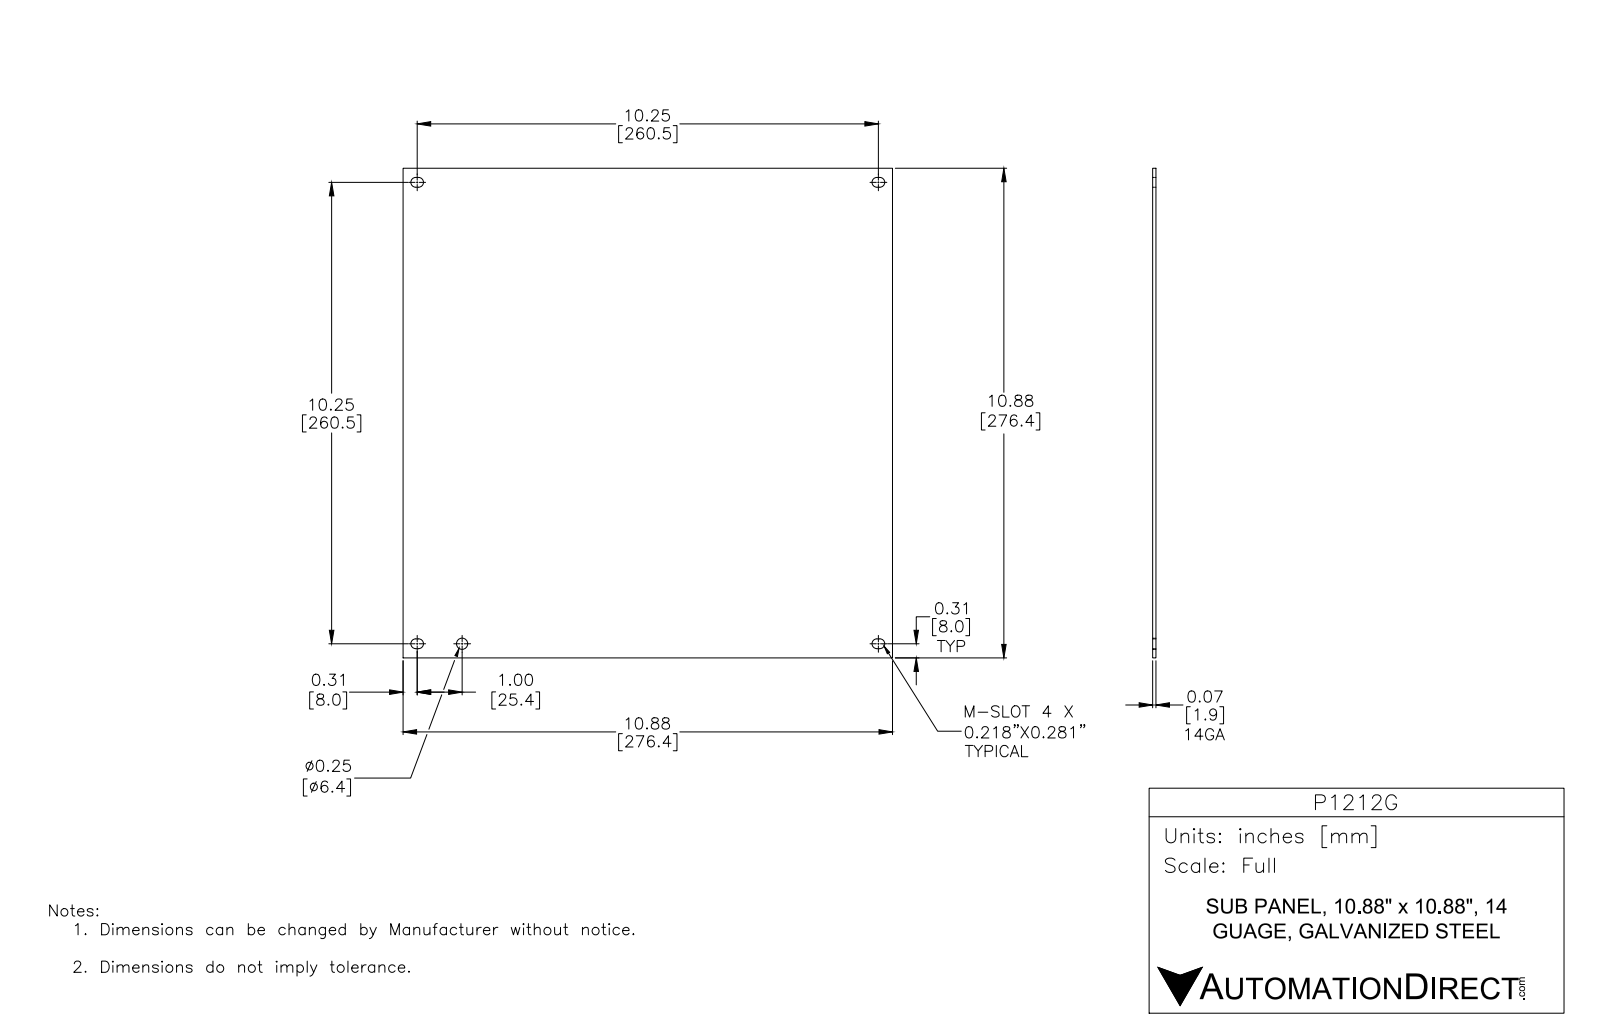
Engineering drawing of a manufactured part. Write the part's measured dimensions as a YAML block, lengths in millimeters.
part_name: "P1212G"
step_written_by: "Autodesk Inventor 2012 (AUTOMOTIVE_DESIGN)"
units: millimeters
bodies: {solids: 1, faces: 23, planar: 14, cylindrical: 9, other: 0}
overall_size: [276.4, 276.4, 1.9]
volume: 143200
surface_area: 154700
round_holes:
  - {diameter: 6.4, count: 1}
partial_cylinders:
  - {radius: 2.8, count: 8}
face_to_face_distances: [1.9, 276.4, 5.2, 10.7, 265.6, 271.2, 5.5, 260.5, 266, 254.9]
